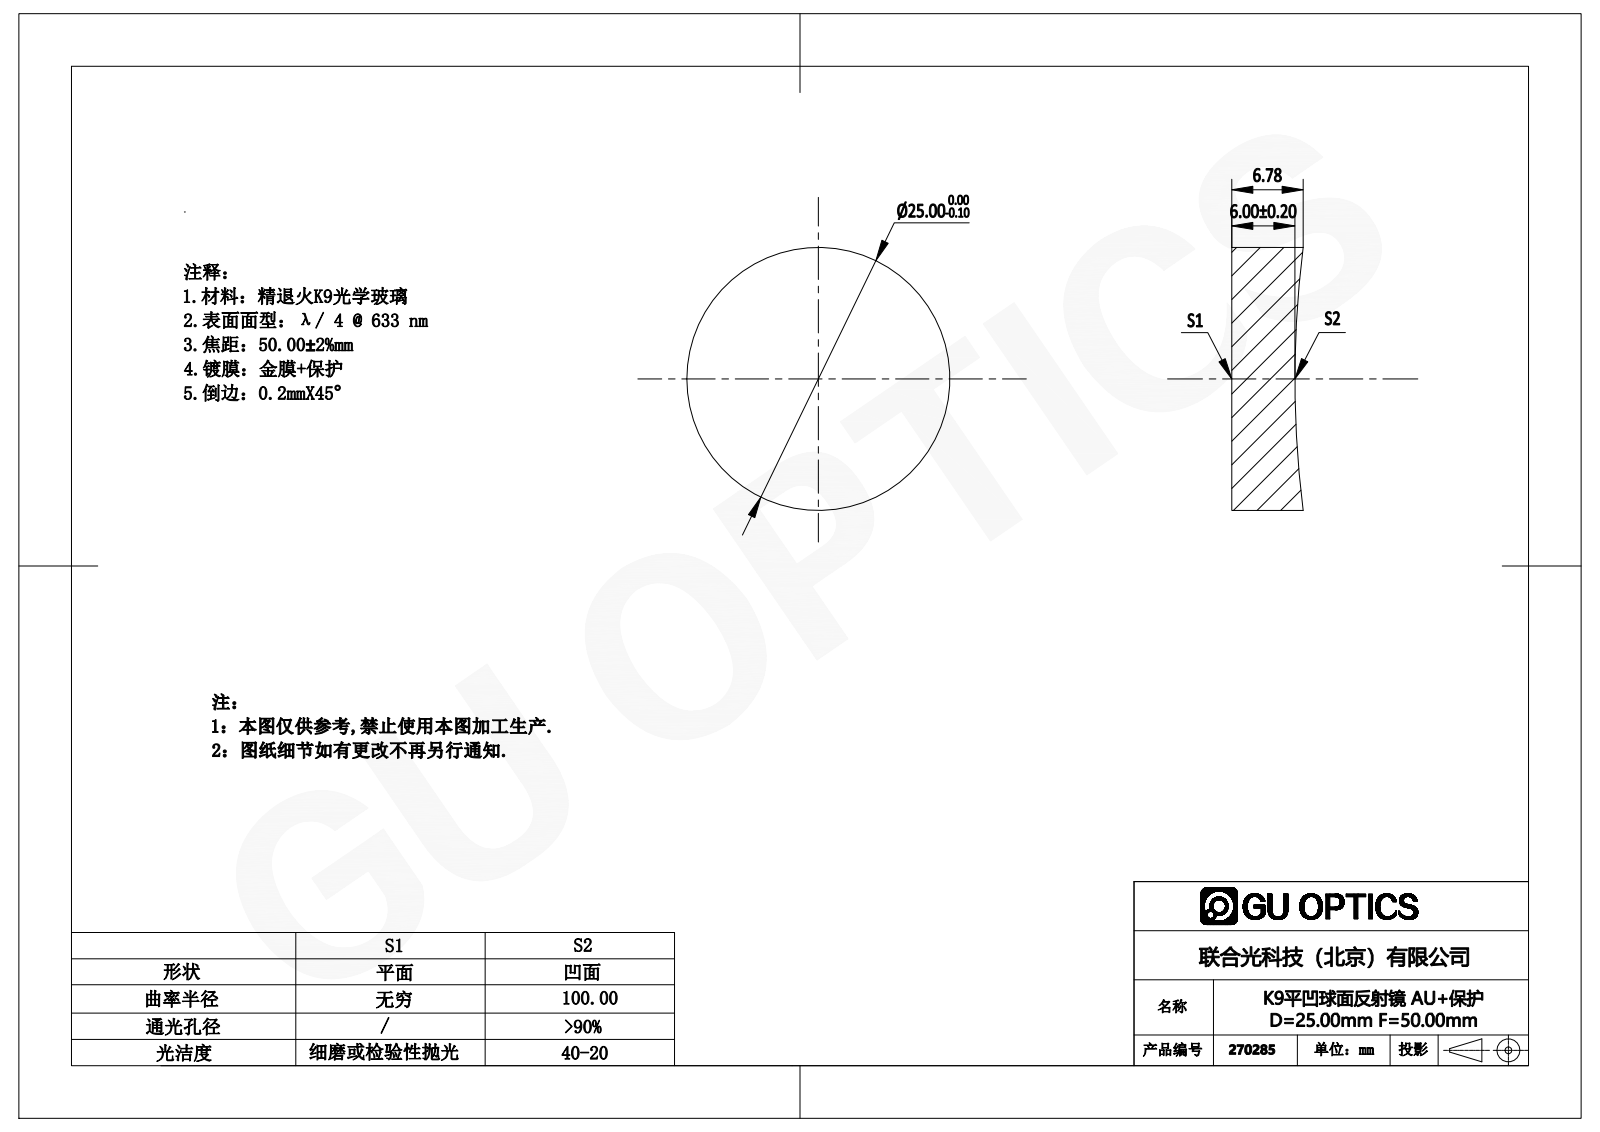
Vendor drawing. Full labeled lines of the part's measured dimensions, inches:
Part name (STEP PRODUCT): 270025
STEP written by: SolidWorks 2016 (AUTOMOTIVE_DESIGN)
Units: inches
Bodies: 1 solid, 5 faces (1 planar, 2 cylindrical, 2 other)
Overall size (bounding box): 0.984 × 0.984 × 0.267
Volume: 0.191 in³ · Surface area: 2.351 in²
Round bosses / shafts (diameter × count): ⌀0.984 ×1
